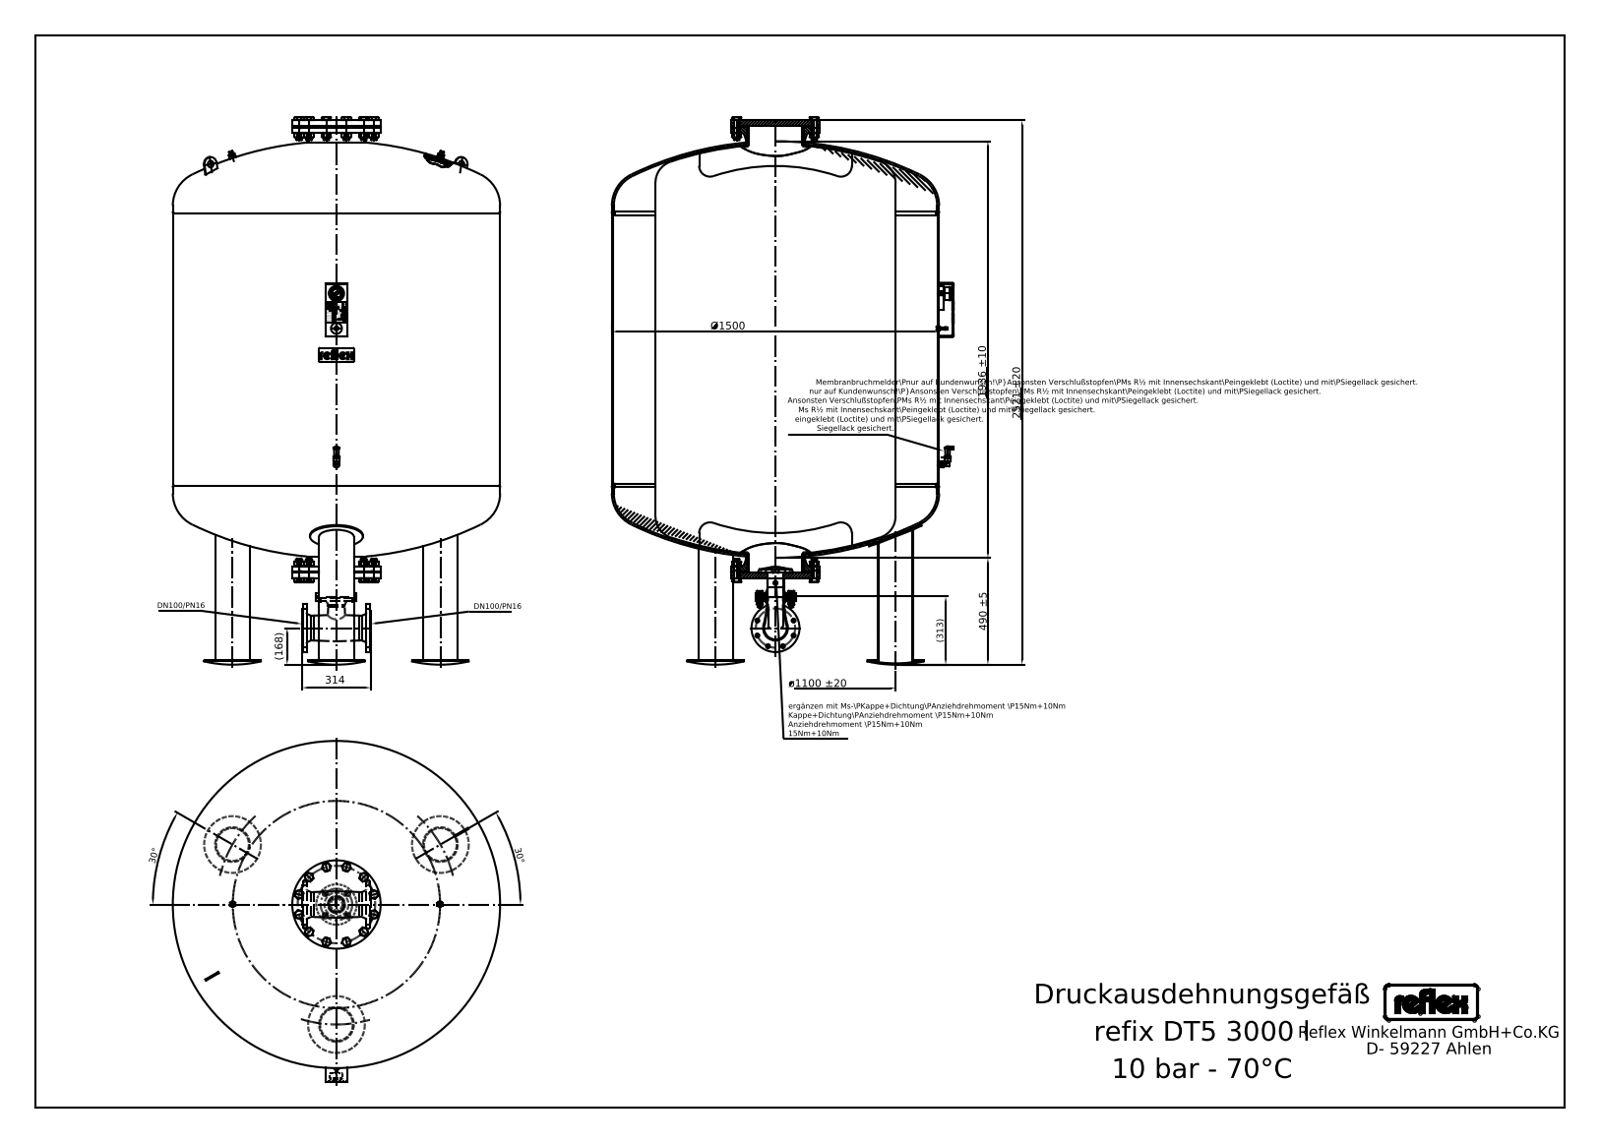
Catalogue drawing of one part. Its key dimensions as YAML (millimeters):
step_written_by: "Mechanical Desktop 2008 (CONFIG_CONTROL_DESIGN)"
units: millimeters
bodies: {solids: 28, faces: 1000, planar: 550, cylindrical: 230, other: 220}
overall_size: [2530, 1566, 1500]
volume: 3117000000
surface_area: 21130000
round_holes:
  - {diameter: 19, count: 8}
  - {diameter: 10, count: 1}
  - {diameter: 30, count: 1}
  - {diameter: 50, count: 1}
  - {diameter: 69, count: 1}
  - {diameter: 114.3, count: 1}
  - {diameter: 260.4, count: 1}
round_bosses_or_shafts:
  - {diameter: 16, count: 16}
  - {diameter: 159, count: 3}
  - {diameter: 28, count: 2}
  - {diameter: 26, count: 2}
  - {diameter: 20, count: 2}
  - {diameter: 1500, count: 1}
  - {diameter: 405, count: 1}
  - {diameter: 273, count: 1}
partial_cylinders:
  - {radius: 5.62, count: 4}
  - {radius: 2.25, count: 3}
  - {radius: 1, count: 2}
  - {radius: 3.84, count: 2}
  - {radius: 5, count: 2}
  - {radius: 6.75, count: 2}
  - {radius: 9.27, count: 2}
  - {radius: 9.4, count: 2}
face_to_face_distances: [1276, 26, 2088, 31, 2057, 57, 424, 1700, 2031, 388]
hole_center_spacings: [90, 127.28, 166.3, 68.88, 68.89, 180, 82.33, 765.5]
